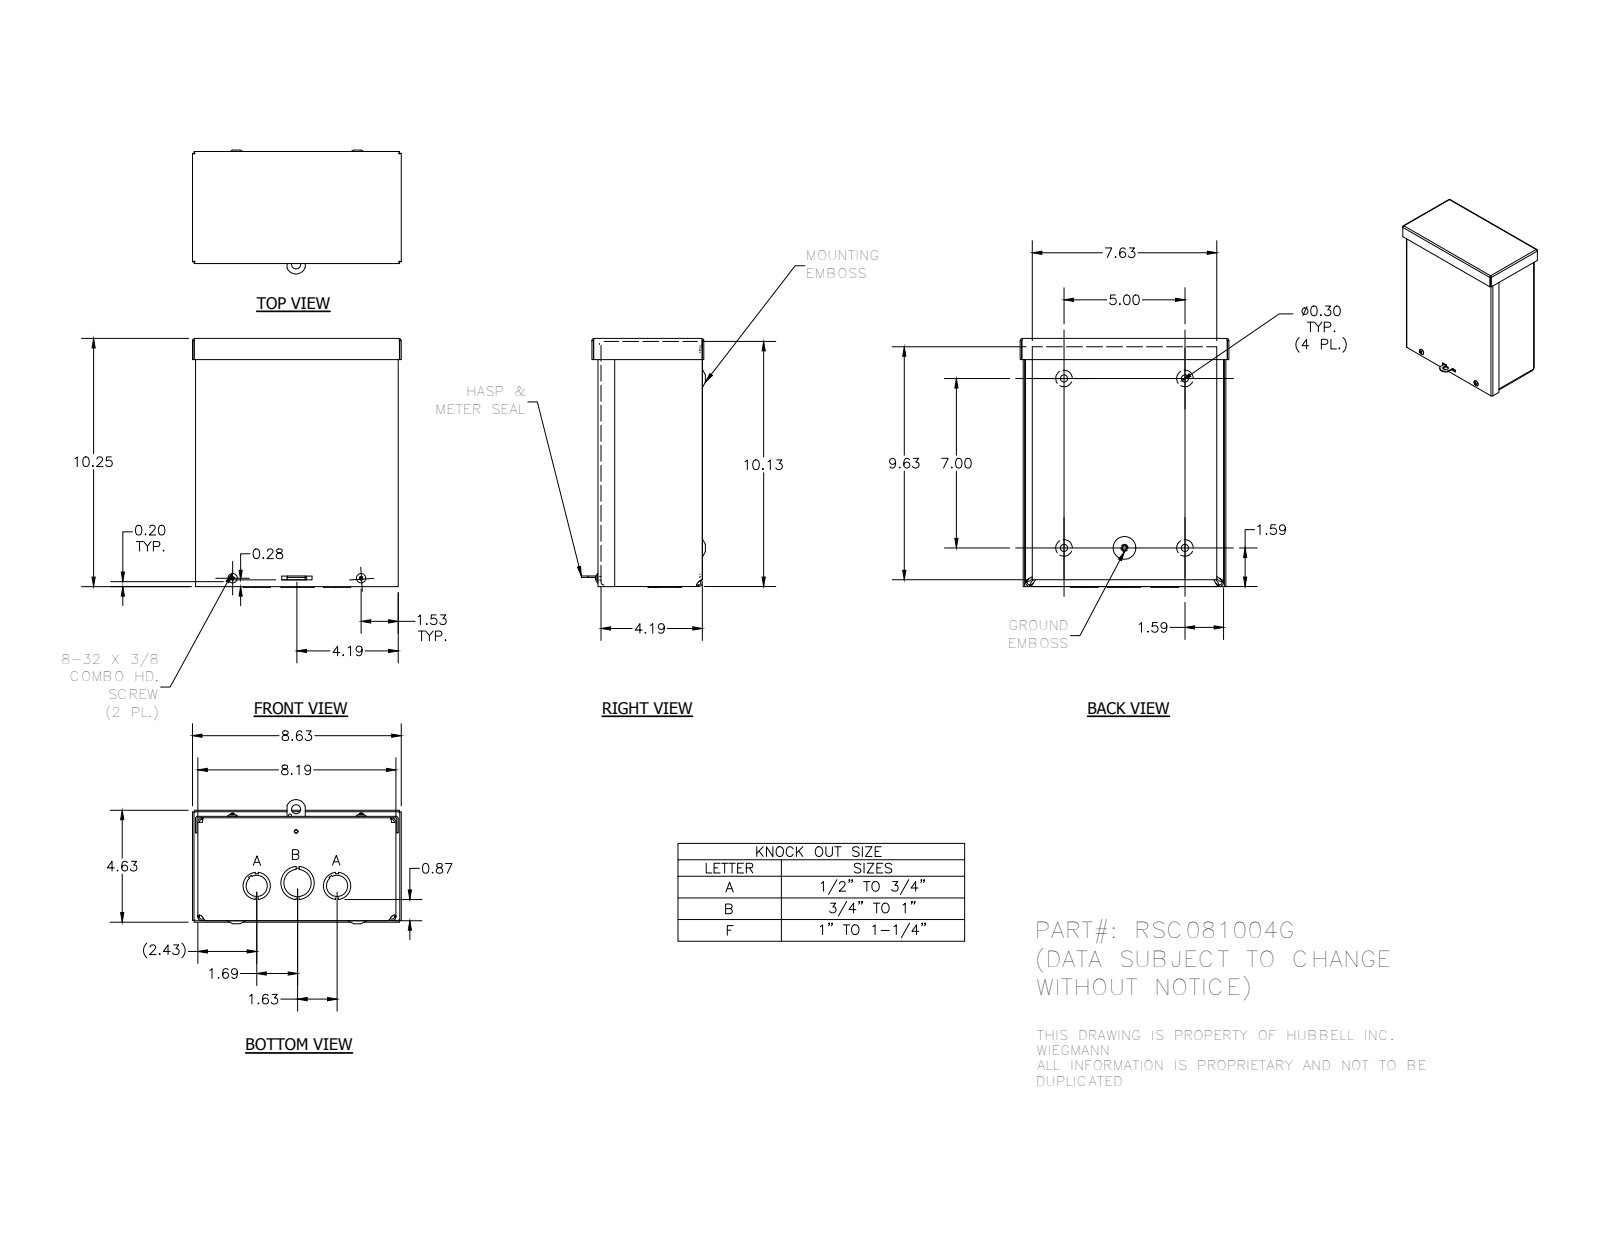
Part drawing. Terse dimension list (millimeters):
name: RSC081004G_WRAP; RSC0810G_LID; RSC0804G_CAP; 3183 (+4 more)
written by: Autodesk Inventor 2014 (AUTOMOTIVE_DESIGN)
unit: mm
bodies: 7 solids, 503 faces (238 planar, 121 cylindrical, 144 other)
size: 261.12 × 219.07 × 130.17
volume: 438 705 mm³; area: 566 397 mm²
holes: 4× ⌀7.62, 4× ⌀7.95, 3× ⌀28.57, 2× ⌀3.17, 2× ⌀3.76, 2× ⌀22.22, 1× ⌀3.96, 1× ⌀4.19, 1× ⌀9.52, 1× ⌀34.92
bosses: 2× ⌀9.75, 2× ⌀4.17, 1× ⌀5.8
rounds: 10× R0.25, 8× R0.79, 8× R2.37, 8× R3.17, 8× R4.75, 4× R0.53, 4× R0.79, 4× R1.4
face distances: 1.58, 1.57, 107.93, 106.35, 206.39, 1.59, 109.52, 107.94, 257.19, 3.15
hole spacings: 27.24, 32.03, 63.5, 127, 134.95, 177.8, 188.79, 204.79
